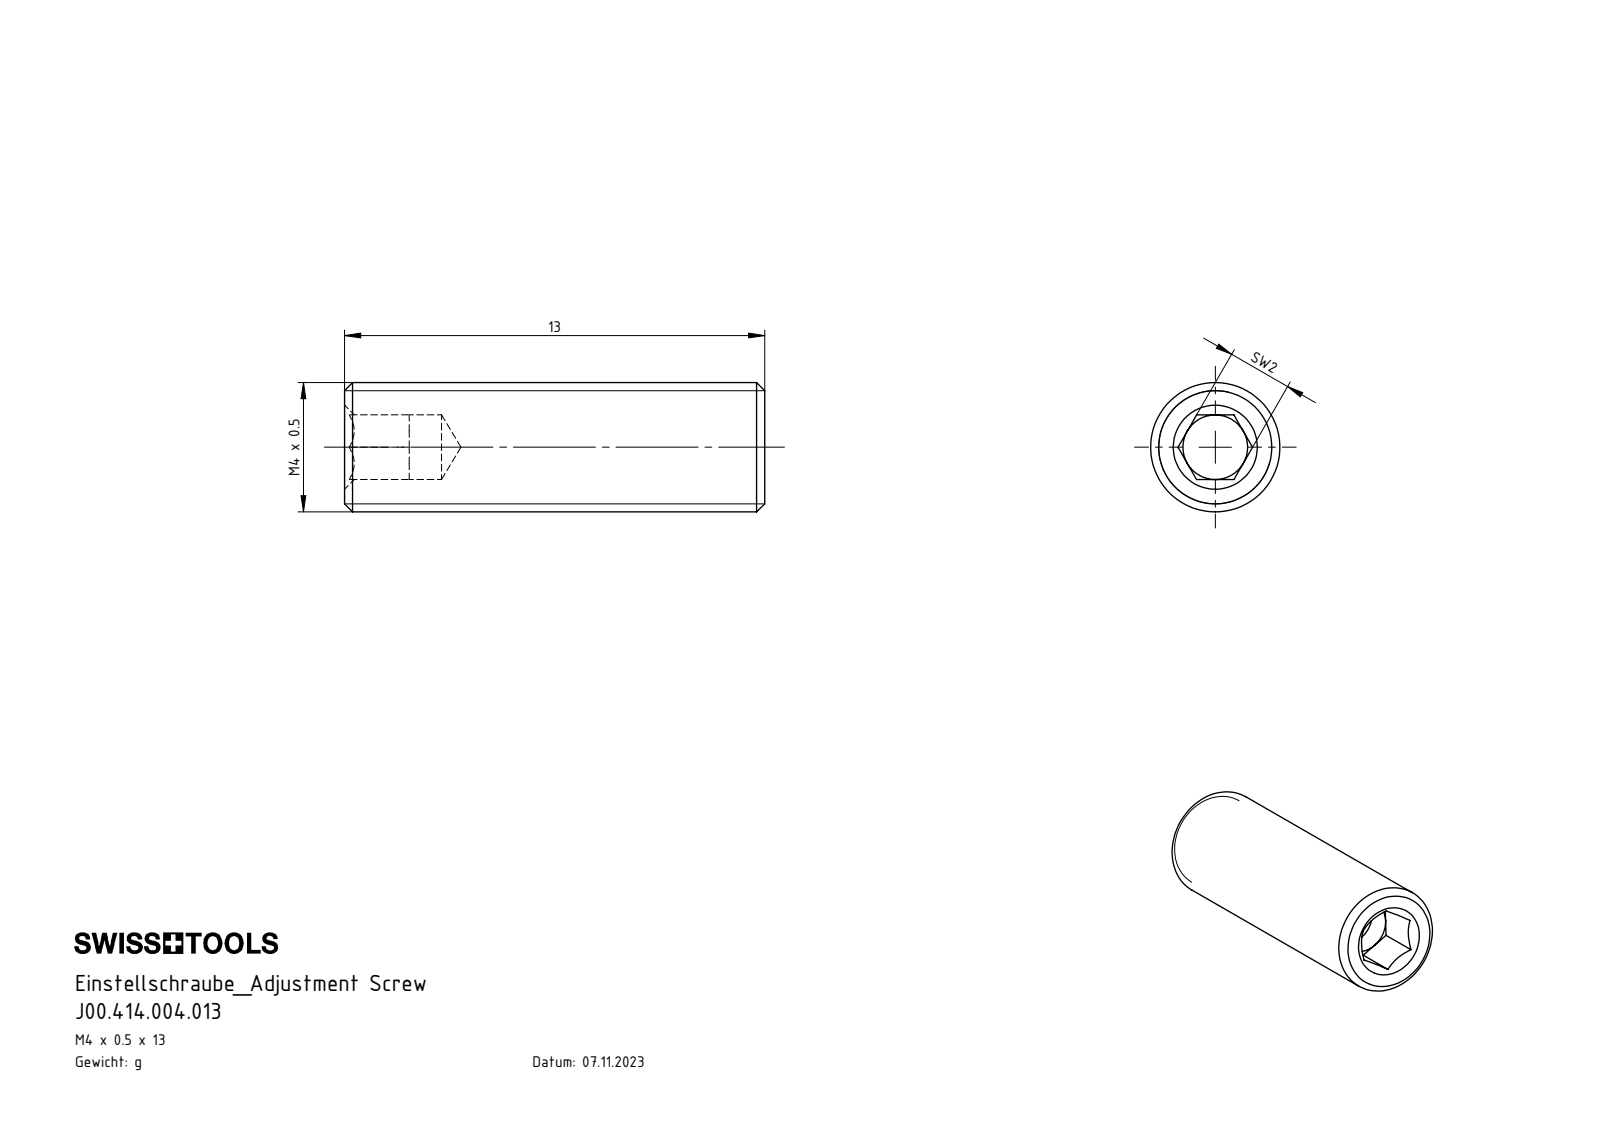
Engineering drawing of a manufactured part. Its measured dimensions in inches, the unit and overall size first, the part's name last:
Units: inches
Overall size (bounding box): 0.512 × 0.157 × 0.157
Round holes (diameter × count): ⌀0.079 ×1
Round bosses / shafts (diameter × count): ⌀0.157 ×1
Main face-to-face distances: 0.079, 0.512, 0.433
Volume: 0.009 in³ · Surface area: 0.316 in²
Bodies: 1 solid, 26 faces (14 planar, 4 cylindrical, 8 other)
Part name (STEP PRODUCT): J00.414.004.013
STEP written by: SolidWorks 2022 (AUTOMOTIVE_DESIGN)
